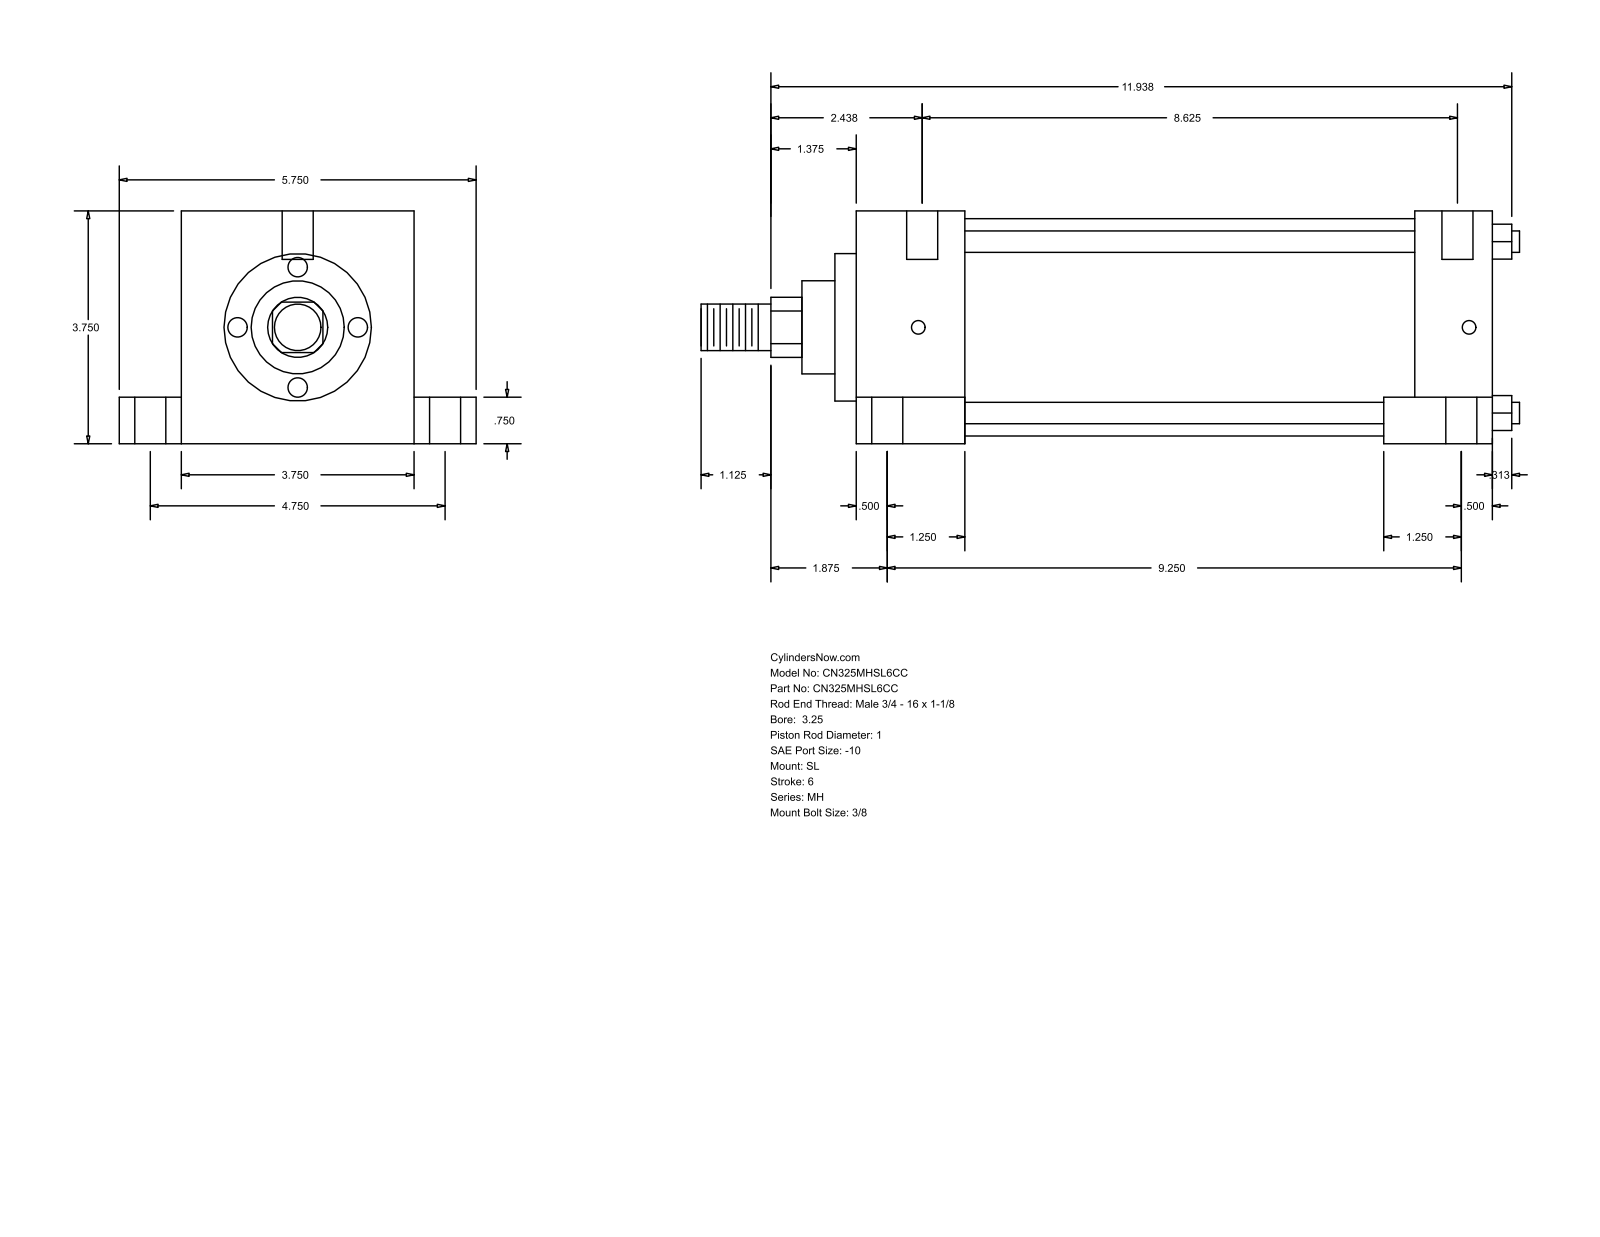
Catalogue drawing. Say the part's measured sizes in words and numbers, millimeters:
The part is named "MH_SL__0325_1". Its 3-D file was written by "GSSL Pune (CONFIG_CONTROL_DESIGN)". It is 0 solids with 110 faces: 77 planar, 33 cylindrical and 0 other. Overall it measures 334.96 by 146.05 by 95.25 millimeters. Round holes: 6 of diameter 12.7, 4 of diameter 5.56, 4 of diameter 19.05. Round bosses or shafts: 4 of diameter 8.76, 1 of diameter 88.9, 1 of diameter 60.33, 1 of diameter 38.1, 1 of diameter 25.4, 1 of diameter 19.05. Partial cylindrical surfaces (rounded edges, fillets, slot ends): 1 of radius 12.29. The main face-to-face distances are 95.24, 260.35, 44.46, 215.89, 25.41, 120.65, 19.05, 76.19, 228.6, 184.14. The hole center spacings are 60.35, 60.41, 61.65, 62, 120.66, 225.42, 228.76, 230.28.
